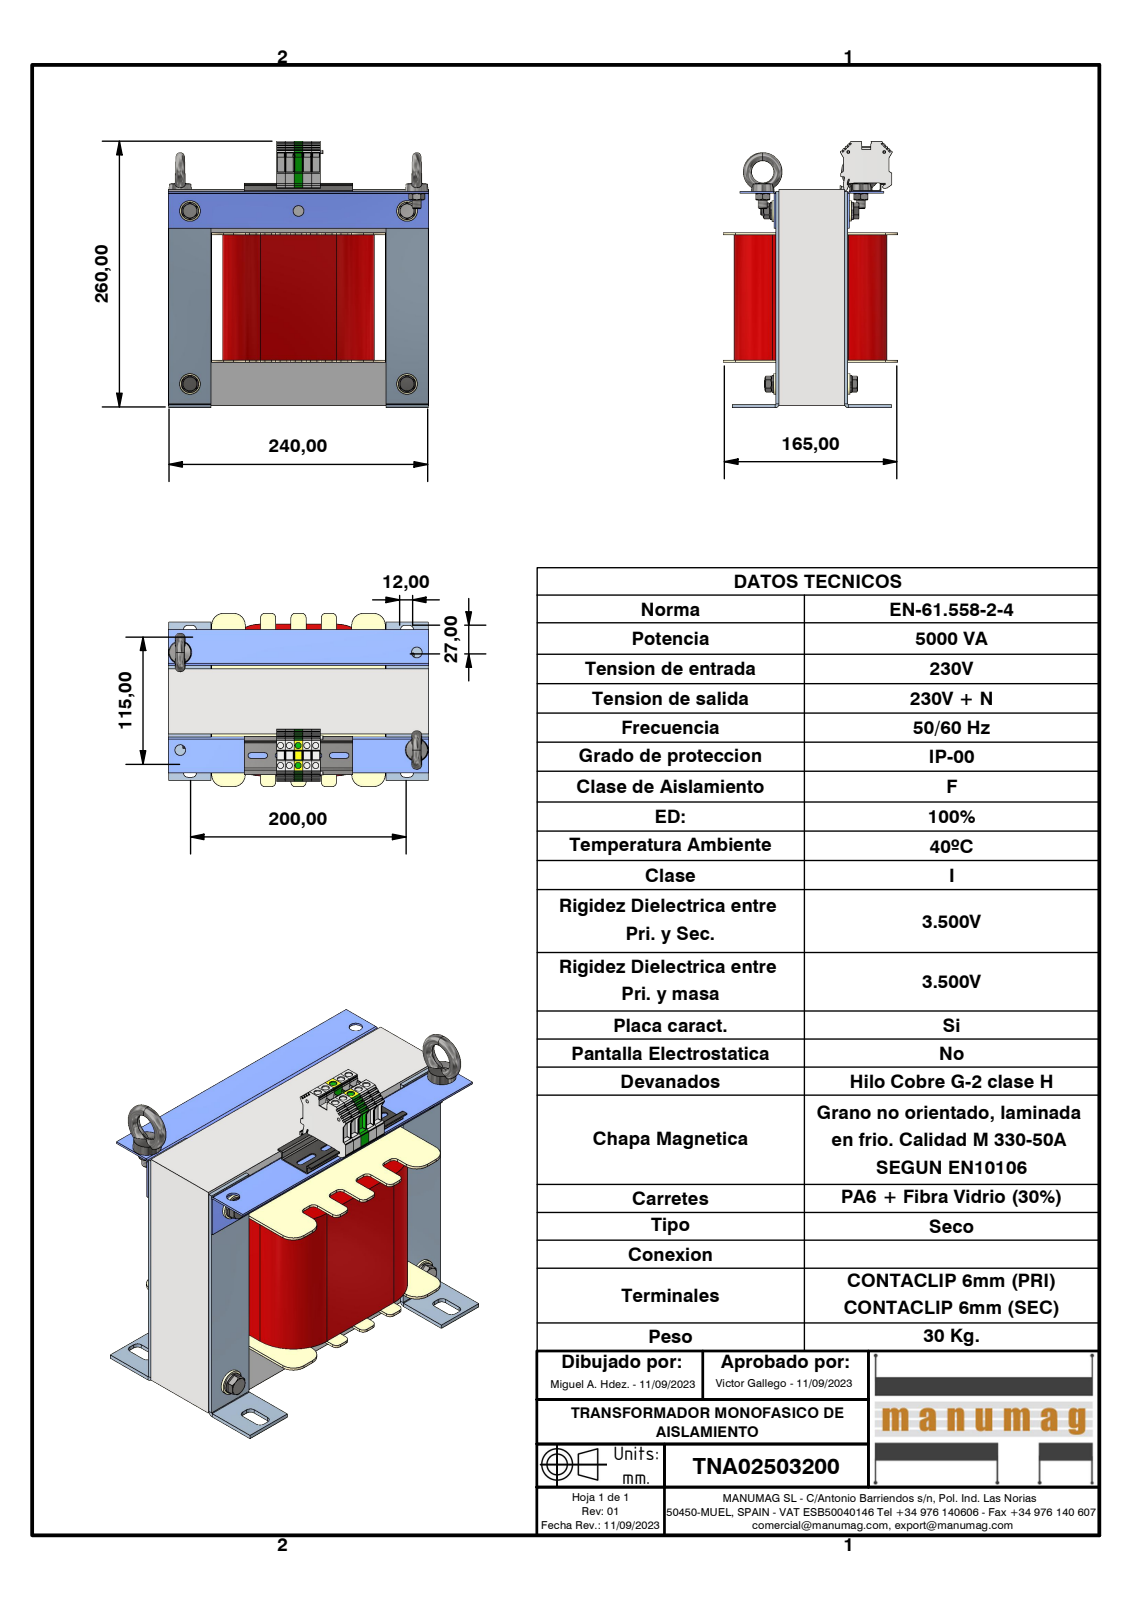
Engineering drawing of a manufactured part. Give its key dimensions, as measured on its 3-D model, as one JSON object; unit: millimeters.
{"part_name": "TNA02503200; EI240 240 x 200 - 60 (Rc80); Escuadra RC80; SEMI 30 X 60 RC80 EI240 - 30 (+8 more)", "step_written_by": "Autodesk Inventor 2023 (AUTOMOTIVE_DESIGN)", "units": "millimeters", "bodies": {"solids": 42, "faces": 1963, "planar": 1282, "cylindrical": 539, "other": 142}, "overall_size": [246.5, 240, 160], "volume_mm3": 4210000, "surface_area_mm2": 535075, "round_holes": [[5.7, 10], [10, 7], [6.65, 6], [8, 4], [8.4, 4], [11, 4], [12, 4], [2.4, 2], [2.5, 2], [2.75, 2]], "round_bosses_or_shafts": [[19, 4], [16, 4], [11.4, 4], [9.6, 4], [7.32, 4], [8, 2], [5.82, 2]], "partial_cylinders_radius": [[0.3, 57], [4, 44], [1, 14], [0.4, 8], [0.5, 8], [2.6, 8], [11, 8], [2, 7]], "face_to_face_distances": [40, 160, 60, 3, 63, 80, 2, 120, 200, 1.5], "hole_center_spacings": [8.1, 20.1, 16.2, 24.52, 18.4, 24.3, 30.48, 32.4]}
